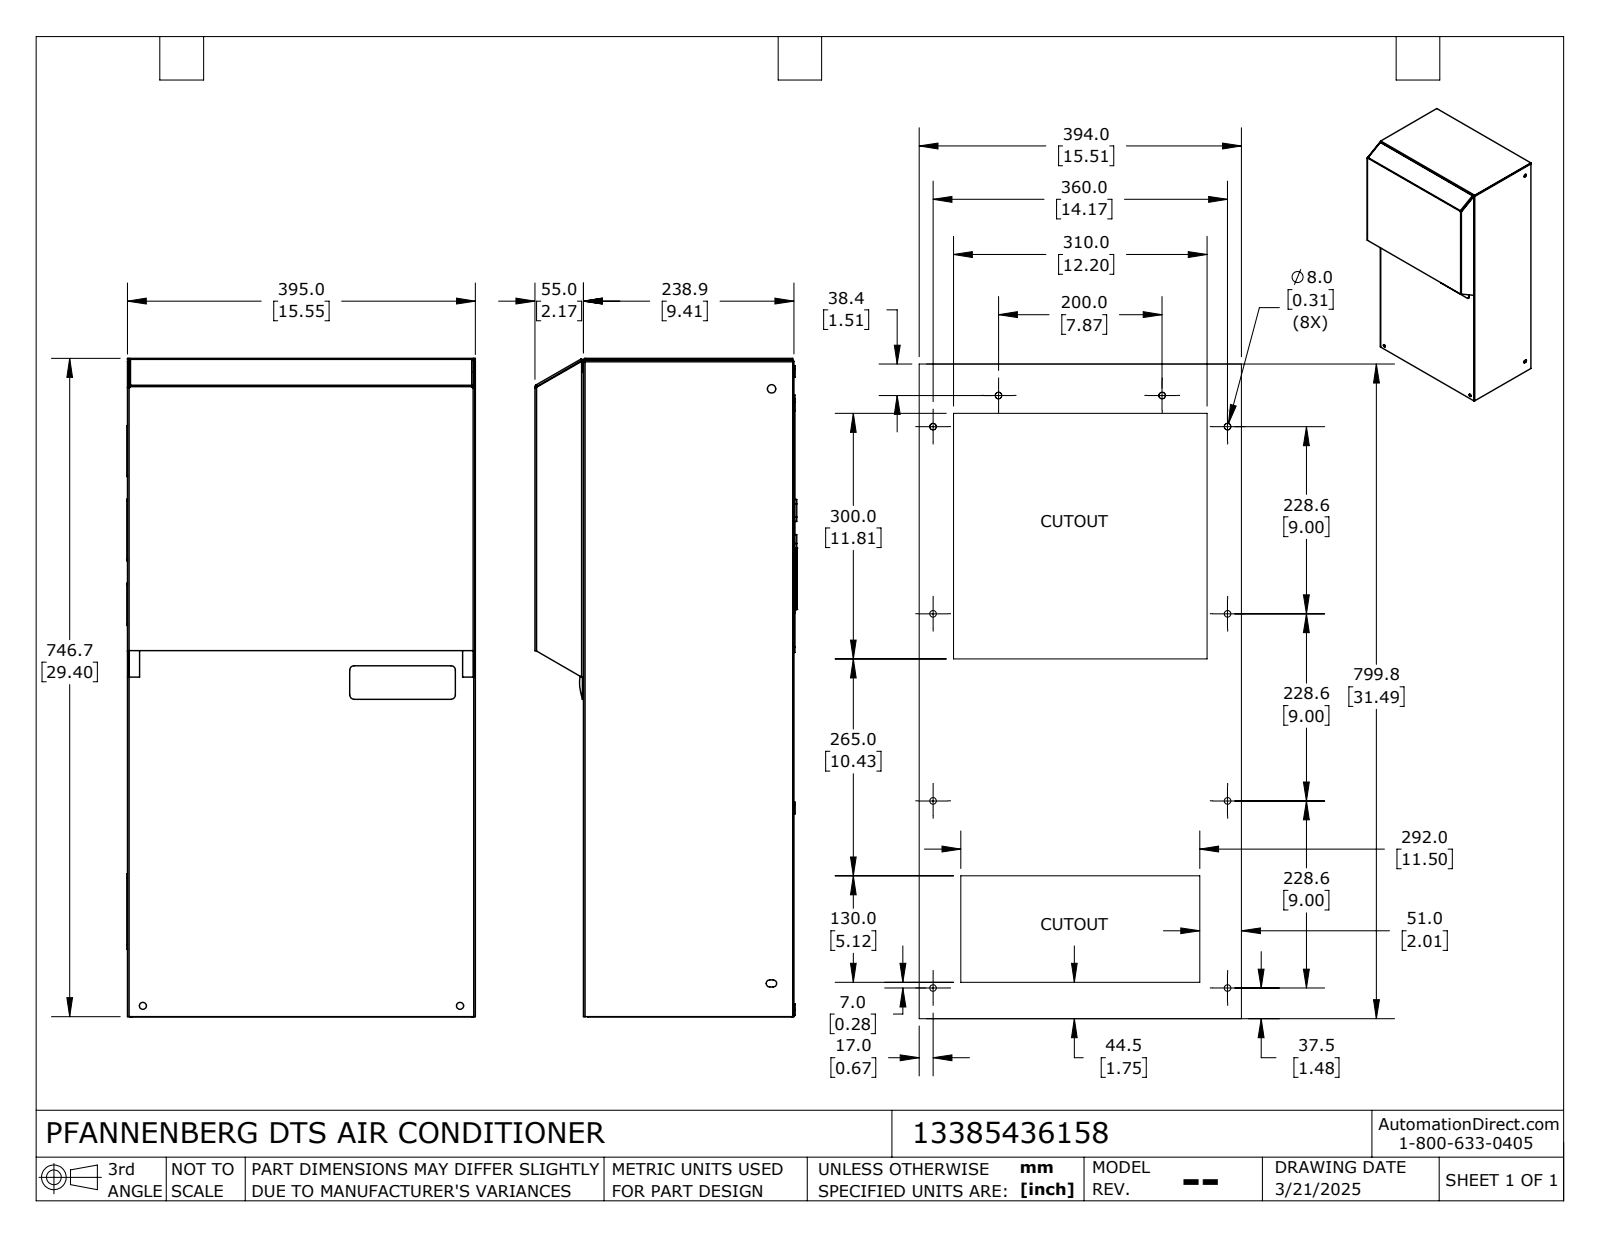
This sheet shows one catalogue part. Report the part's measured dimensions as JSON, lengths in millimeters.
{"part_name": "13385436158_Default", "step_written_by": "SolidWorks 2024 (CONFIG_CONTROL_DESIGN)", "units": "millimeters", "bodies": {"solids": 1, "faces": 1711, "planar": 962, "cylindrical": 722, "other": 27}, "overall_size": [746.7, 395.5, 297.1], "volume_mm3": 70100000, "surface_area_mm2": 2898000, "round_holes": [[4.2, 19], [7.2, 10], [4.1, 8], [4, 6], [5, 4], [6, 2], [8, 2], [11.1, 2], [3, 1], [8.1, 1], [9.5, 1], [21, 1]], "round_bosses_or_shafts": [[13, 10]], "partial_cylinders_radius": [[3.2, 140], [2.8, 129], [0.8, 12], [2, 12], [5, 12], [2, 11], [2.9, 11], [5, 10]], "face_to_face_distances": [1.2, 0.8, 2, 235.7, 236.4, 237.6, 1.3, 236.9, 237.7, 238.9], "hole_center_spacings": [728.3, 27.2, 28.8, 43.5, 100, 200.3, 227, 228.9]}
